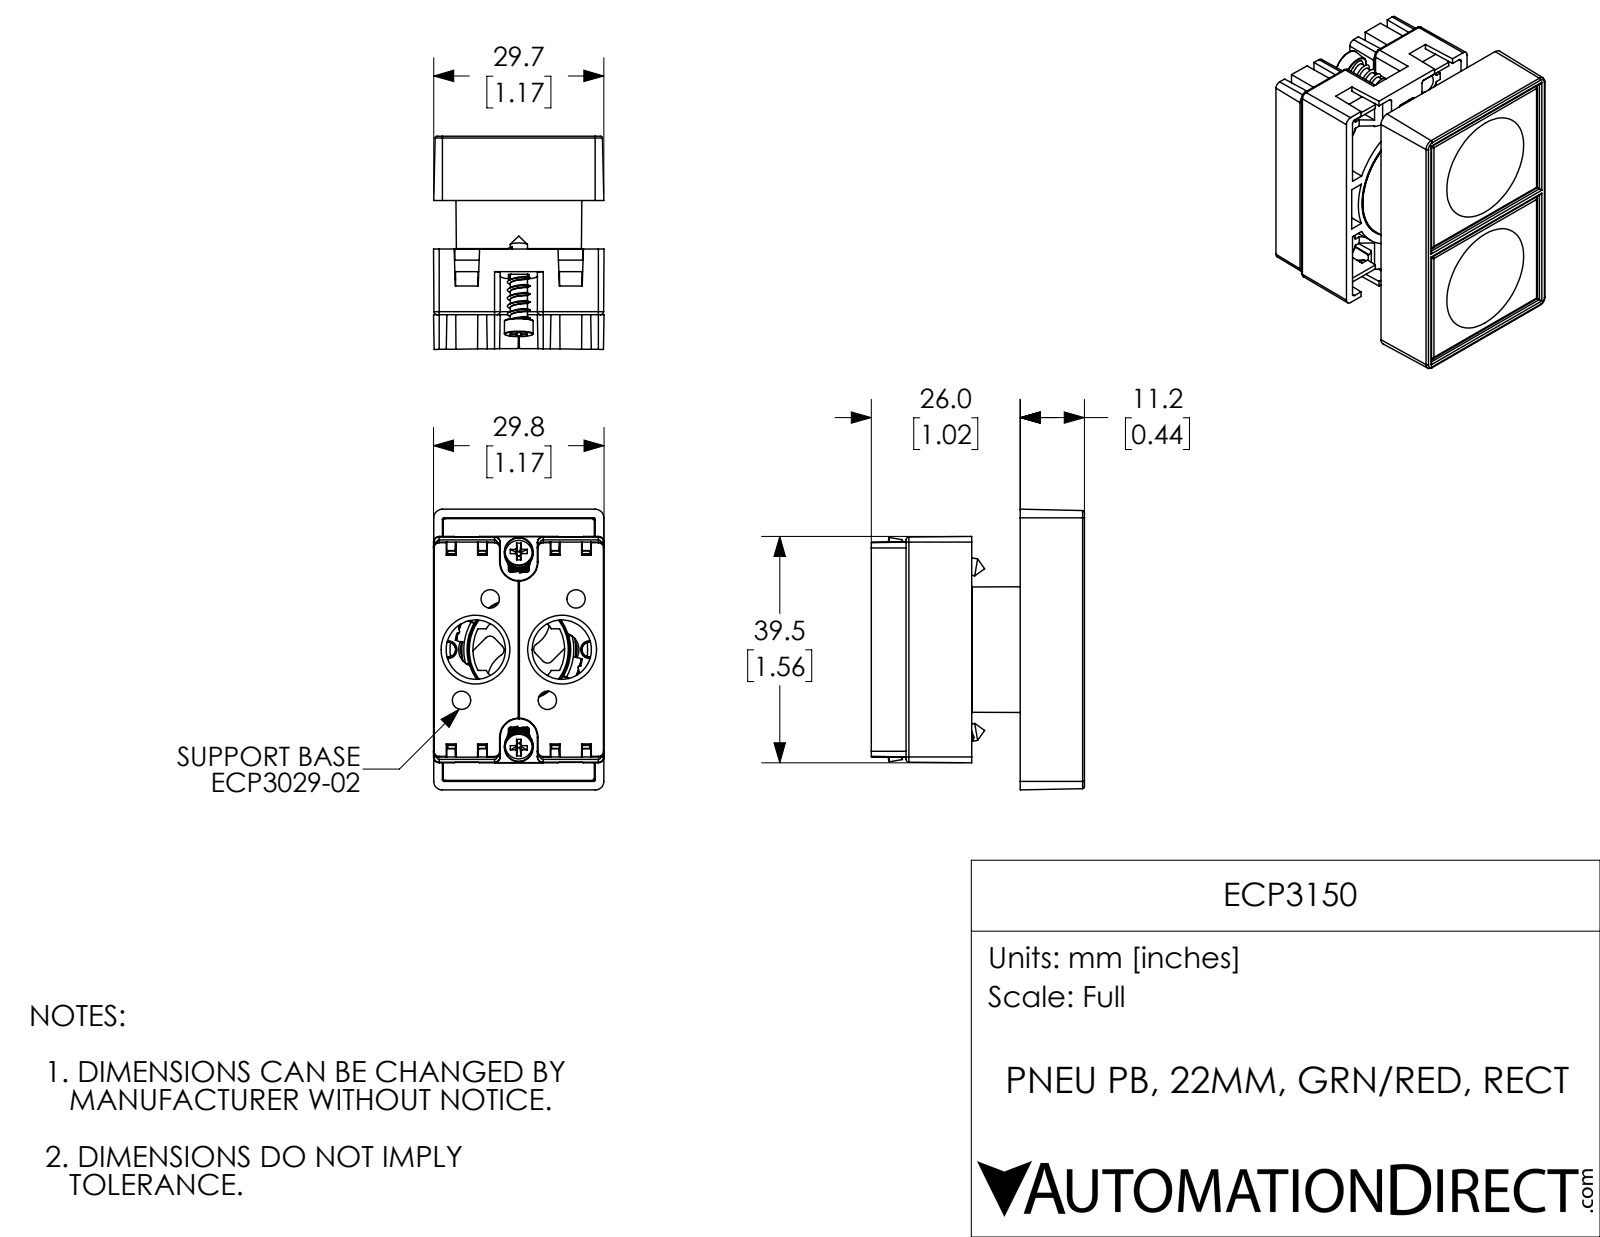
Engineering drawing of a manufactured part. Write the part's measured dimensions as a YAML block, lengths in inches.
part_name: "ECP3150"
step_written_by: "SolidWorks 2017 (AUTOMOTIVE_DESIGN)"
units: inches
bodies: {solids: 8, faces: 877, planar: 401, cylindrical: 181, other: 295}
overall_size: [1.929, 1.465, 1.173]
volume: 1.099
surface_area: 36.92
round_holes:
  - {diameter: 0.081, count: 4}
  - {diameter: 0.315, count: 2}
  - {diameter: 0.407, count: 2}
  - {diameter: 0.697, count: 1}
  - {diameter: 0.756, count: 1}
round_bosses_or_shafts:
  - {diameter: 0.374, count: 2}
  - {diameter: 0.197, count: 2}
  - {diameter: 0.118, count: 2}
  - {diameter: 0.866, count: 1}
partial_cylinders:
  - {radius: 0.012, count: 30}
  - {radius: 0.02, count: 24}
  - {radius: 0.039, count: 12}
  - {radius: 0.006, count: 8}
  - {radius: 0.008, count: 4}
  - {radius: 0.008, count: 2}
  - {radius: 0.118, count: 2}
  - {radius: 0.128, count: 2}
face_to_face_distances: [0.059, 1.135, 0.232, 0.903, 0.291, 0.844, 0.067, 0.079, 0.37, 0.311]
hole_center_spacings: [0.304, 0.366, 0.487, 0.541, 0.665, 0.817, 0.217, 0.295]
